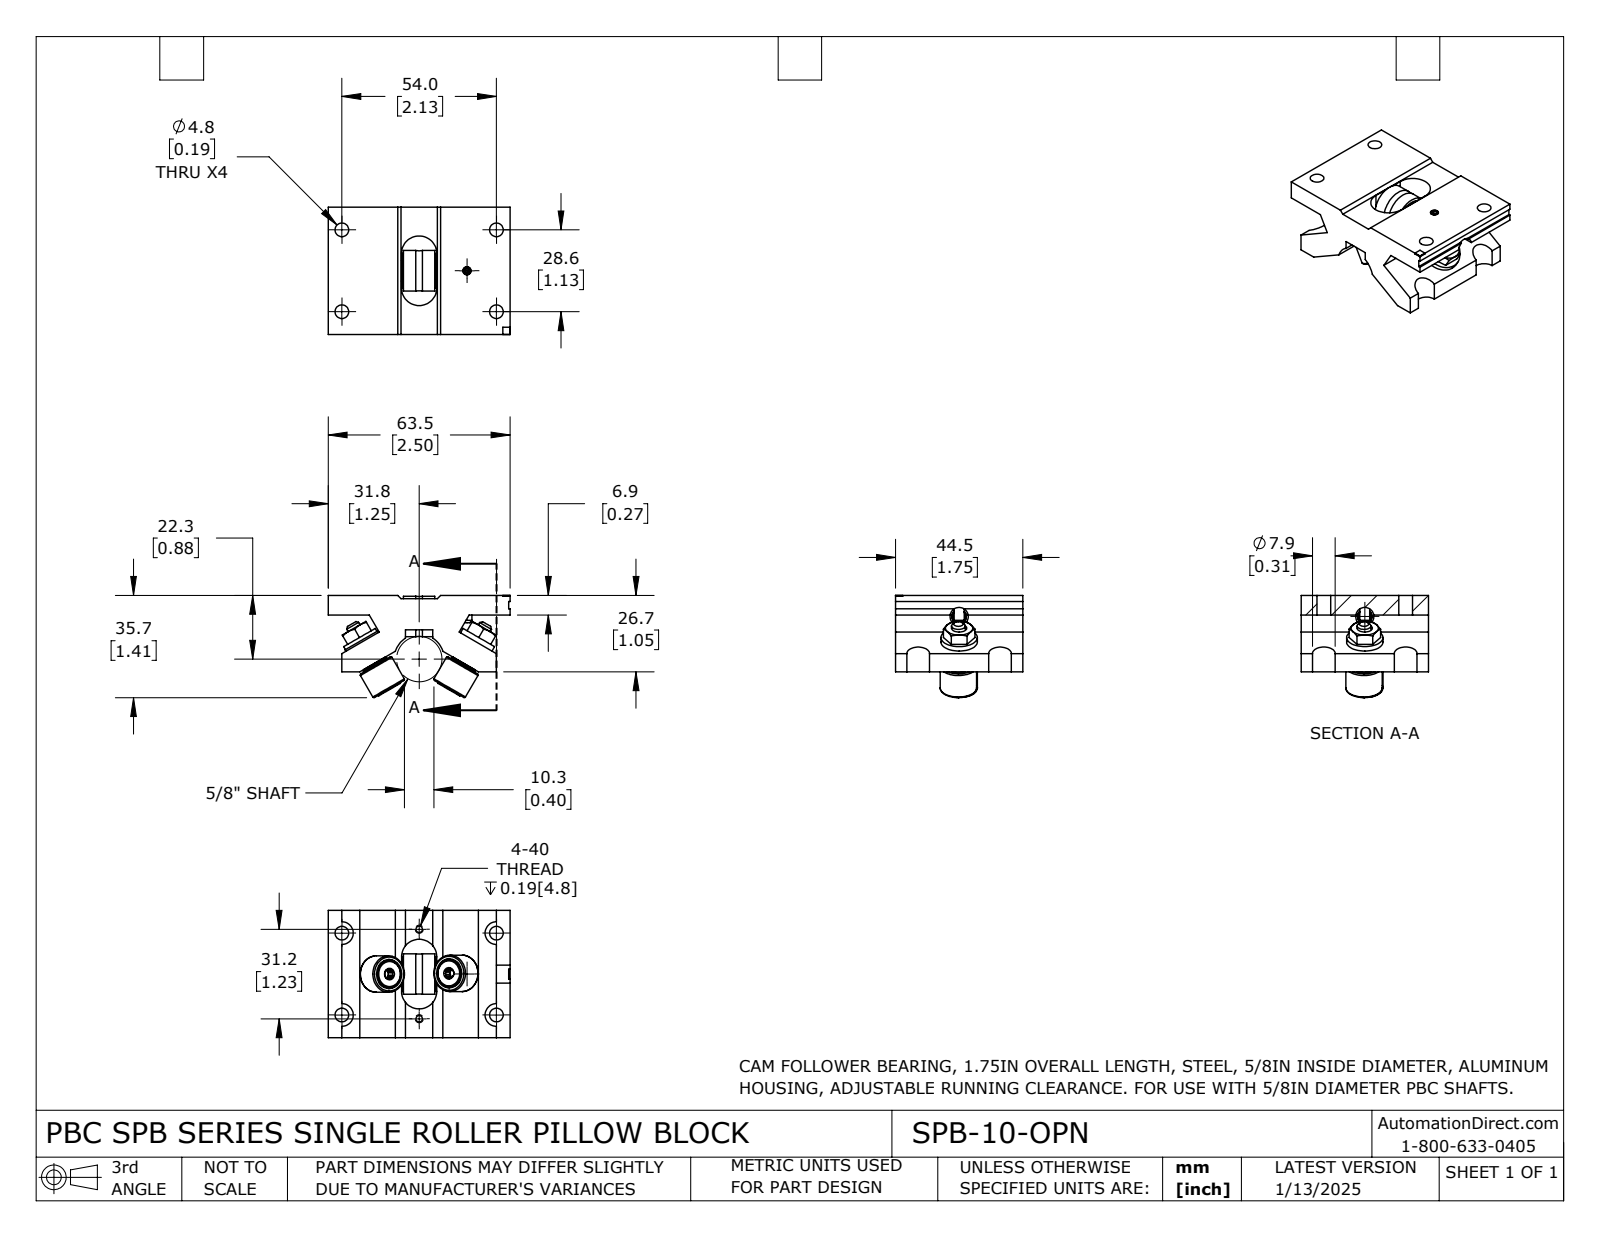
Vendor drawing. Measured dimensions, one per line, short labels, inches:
name: SPB-10-OPN
written by: SolidWorks 2023 (CONFIG_CONTROL_DESIGN)
unit: in
bodies: 11 solids, 324 faces (139 planar, 101 cylindrical, 84 other)
size: 2.5 × 1.75 × 1.405
volume: 2.647 in³; area: 28.33 in²
holes: 4× ⌀0.187, 2× ⌀0.089, 2× ⌀0.129, 2× ⌀0.149, 2× ⌀0.399, 1× ⌀0.107, 1× ⌀0.156, 1× ⌀0.19, 1× ⌀0.193, 1× ⌀0.196, 1× ⌀0.197, 1× ⌀0.2
bosses: 3× ⌀0.5, 2× ⌀0.369, 1× ⌀0.557, 1× ⌀0.515, 1× ⌀0.478, 1× ⌀0.25, 1× ⌀0.2, 1× ⌀0.197
rounds: 4× R0.156, 2× R0.243, 1× R0.344
face distances: 0.34, 0.27, 1.75, 0.78, 1.05, 2.313, 0.187, 1.007, 1.493, 0.82
hole spacings: 1.064, 1.586, 0.693, 0.9, 1.125, 1.81, 2.125, 2.405
